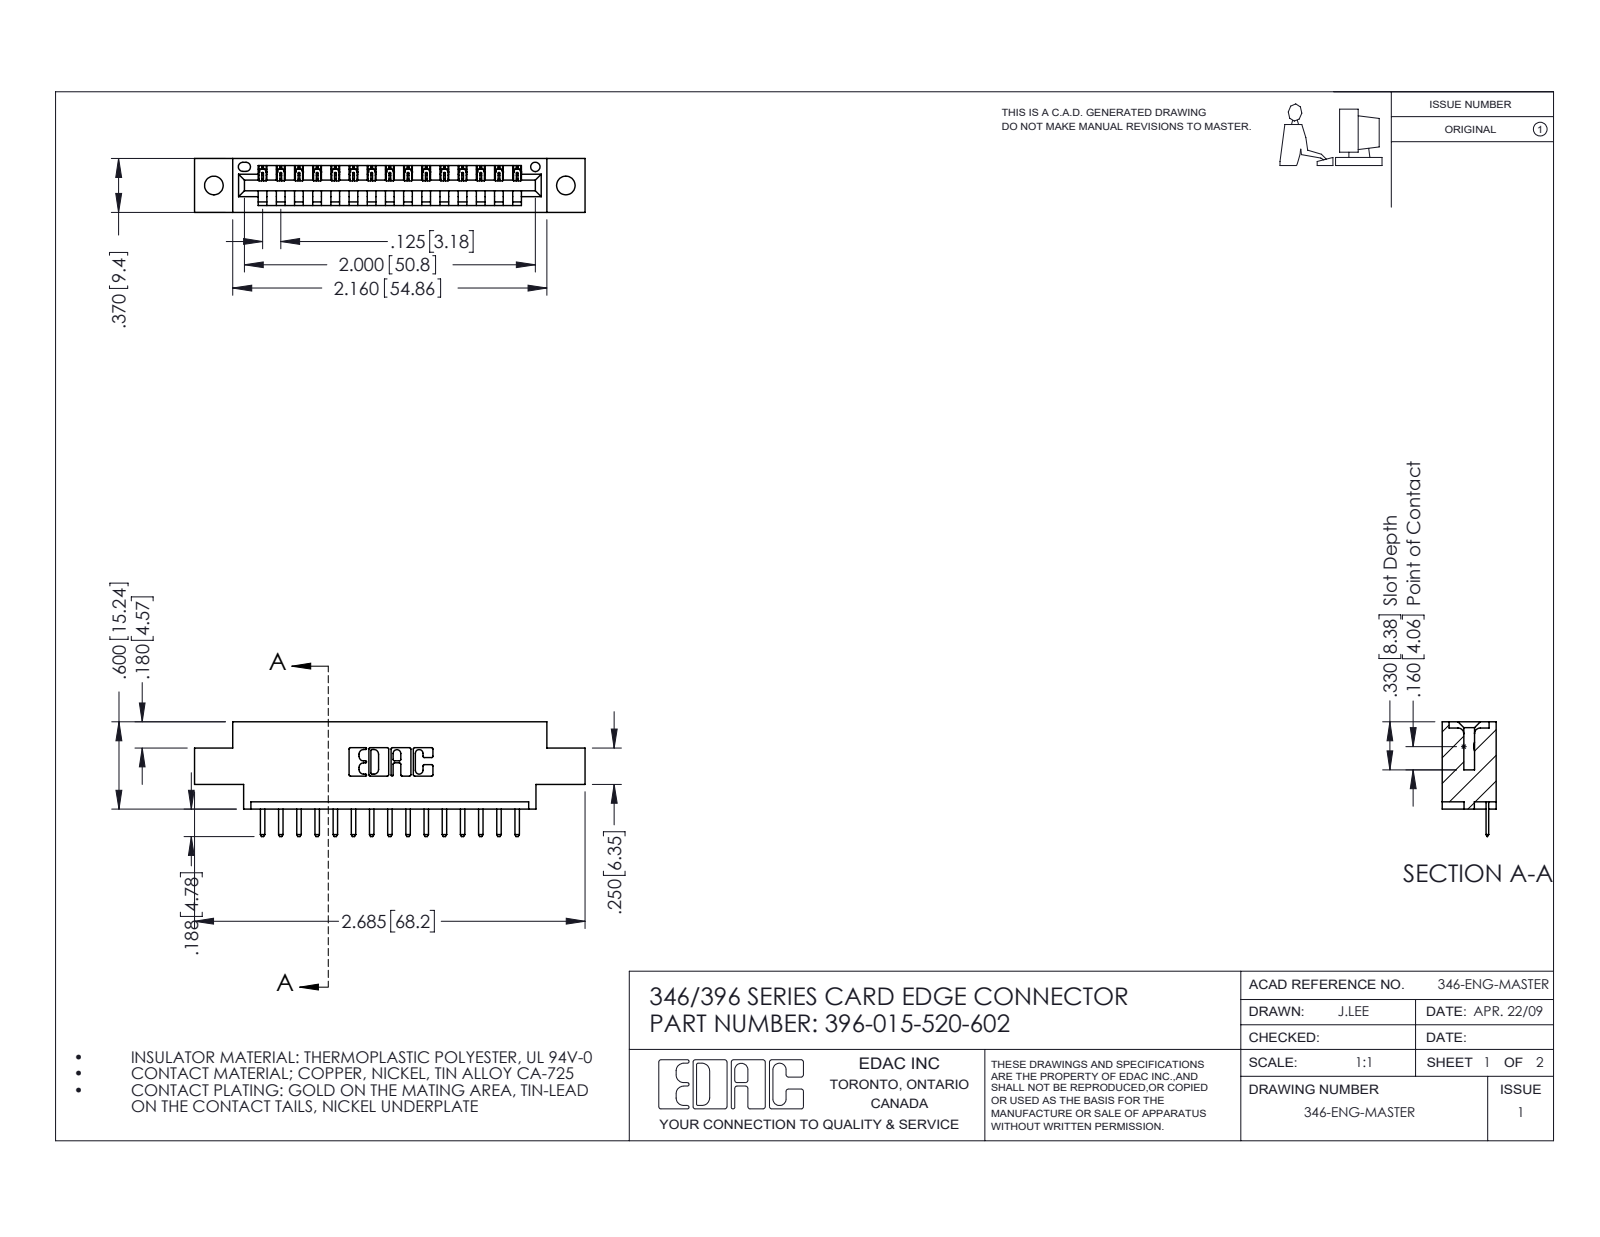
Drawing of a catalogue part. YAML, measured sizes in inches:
part_name: "346 Part_0.170 Offset - 0.128 Dia; 396-015-520-602; 345-292-001_345-293-120"
step_written_by: "SolidWorks 2016 (CONFIG_CONTROL_DESIGN)"
units: inches
bodies: {solids: 16, faces: 1056, planar: 710, cylindrical: 346, other: 0}
overall_size: [2.685, 0.788, 0.37]
volume: 0.373
surface_area: 10.99
round_holes:
  - {diameter: 0.128, count: 2}
  - {diameter: 0.064, count: 1}
partial_cylinders:
  - {radius: 0.01, count: 32}
  - {radius: 0.006, count: 30}
  - {radius: 0.01, count: 22}
  - {radius: 0.007, count: 6}
  - {radius: 0.031, count: 6}
  - {radius: 0.026, count: 3}
  - {radius: 0.031, count: 2}
  - {radius: 0.04, count: 2}
face_to_face_distances: [0.37, 0.048, 0.322, 0.25, 0.148, 0.222, 0.1, 0.174, 0.072, 0.298]
hole_center_spacings: [0.246, 2.213, 2.42]
